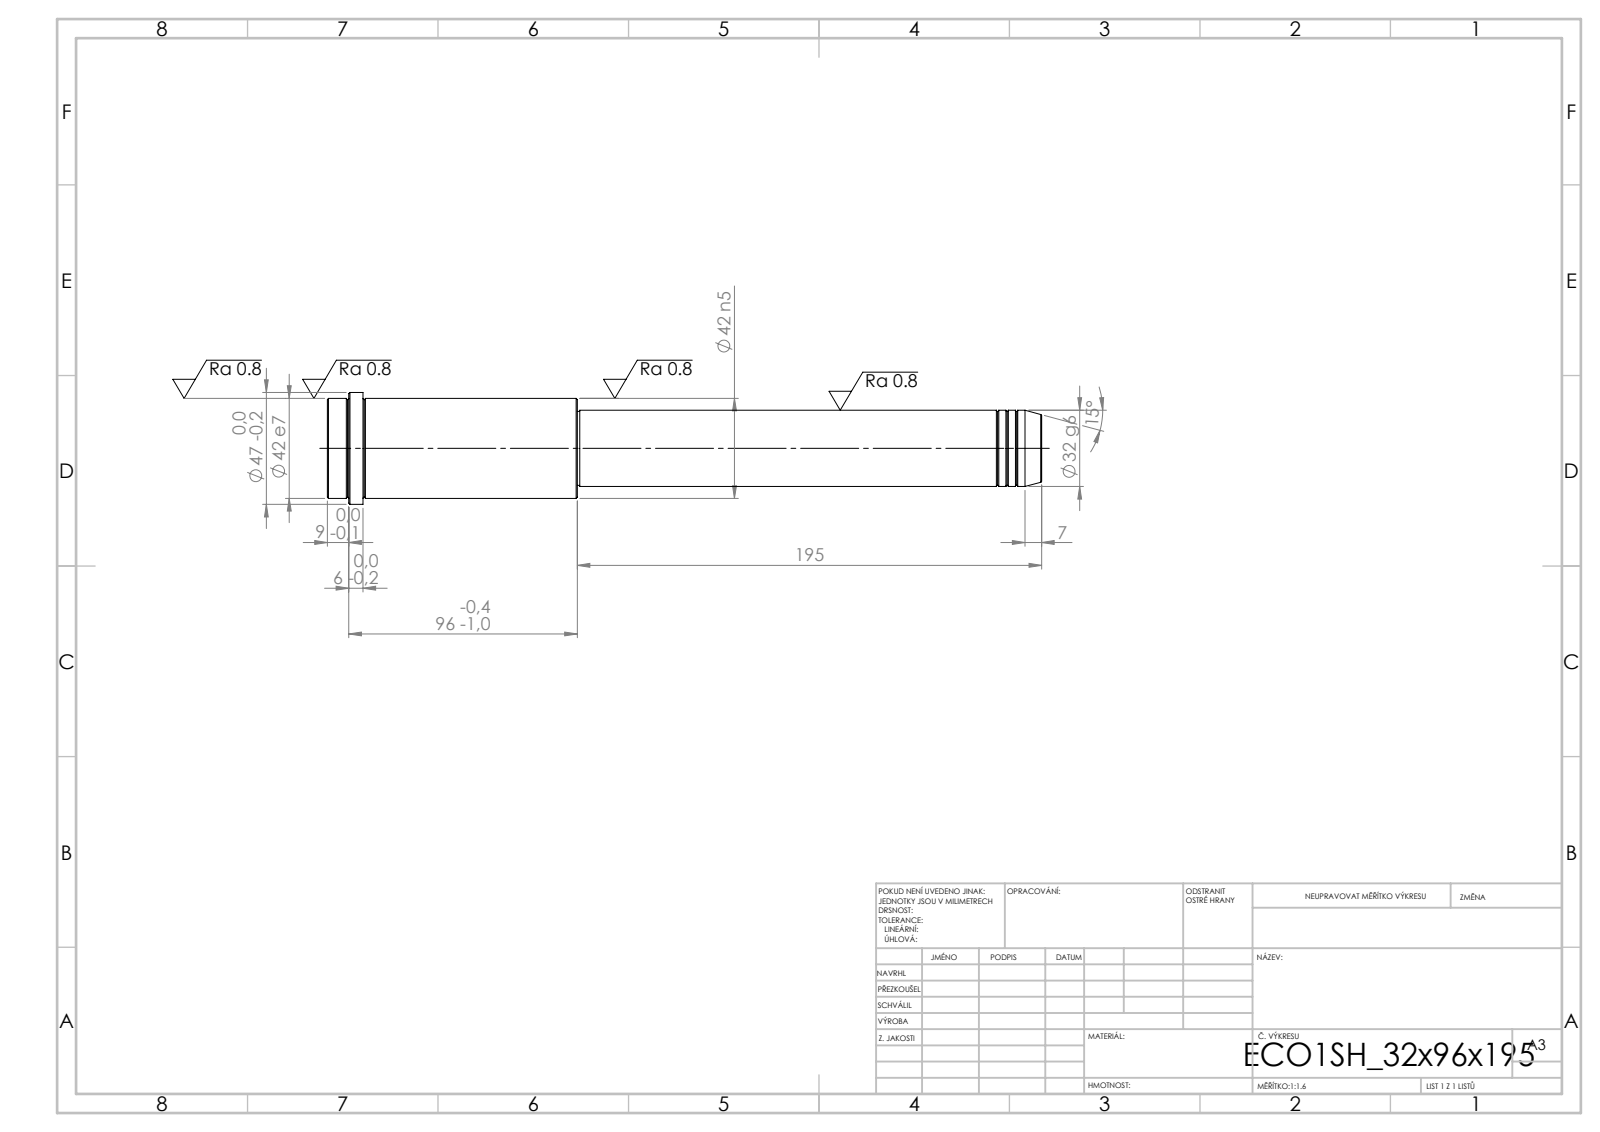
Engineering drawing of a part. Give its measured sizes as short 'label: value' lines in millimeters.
written by: SolidWorks 2019 (CONFIG_CONTROL_DESIGN)
unit: mm
bodies: 1 solid, 52 faces (6 planar, 16 cylindrical, 30 other)
size: 300 × 47 × 47
volume: 303 440 mm³; area: 37 098 mm²
bosses: 1× ⌀47, 1× ⌀42, 1× ⌀32, 1× ⌀31
face distances: 300, 195, 105, 285, 90, 15, 291, 96, 6, 9
